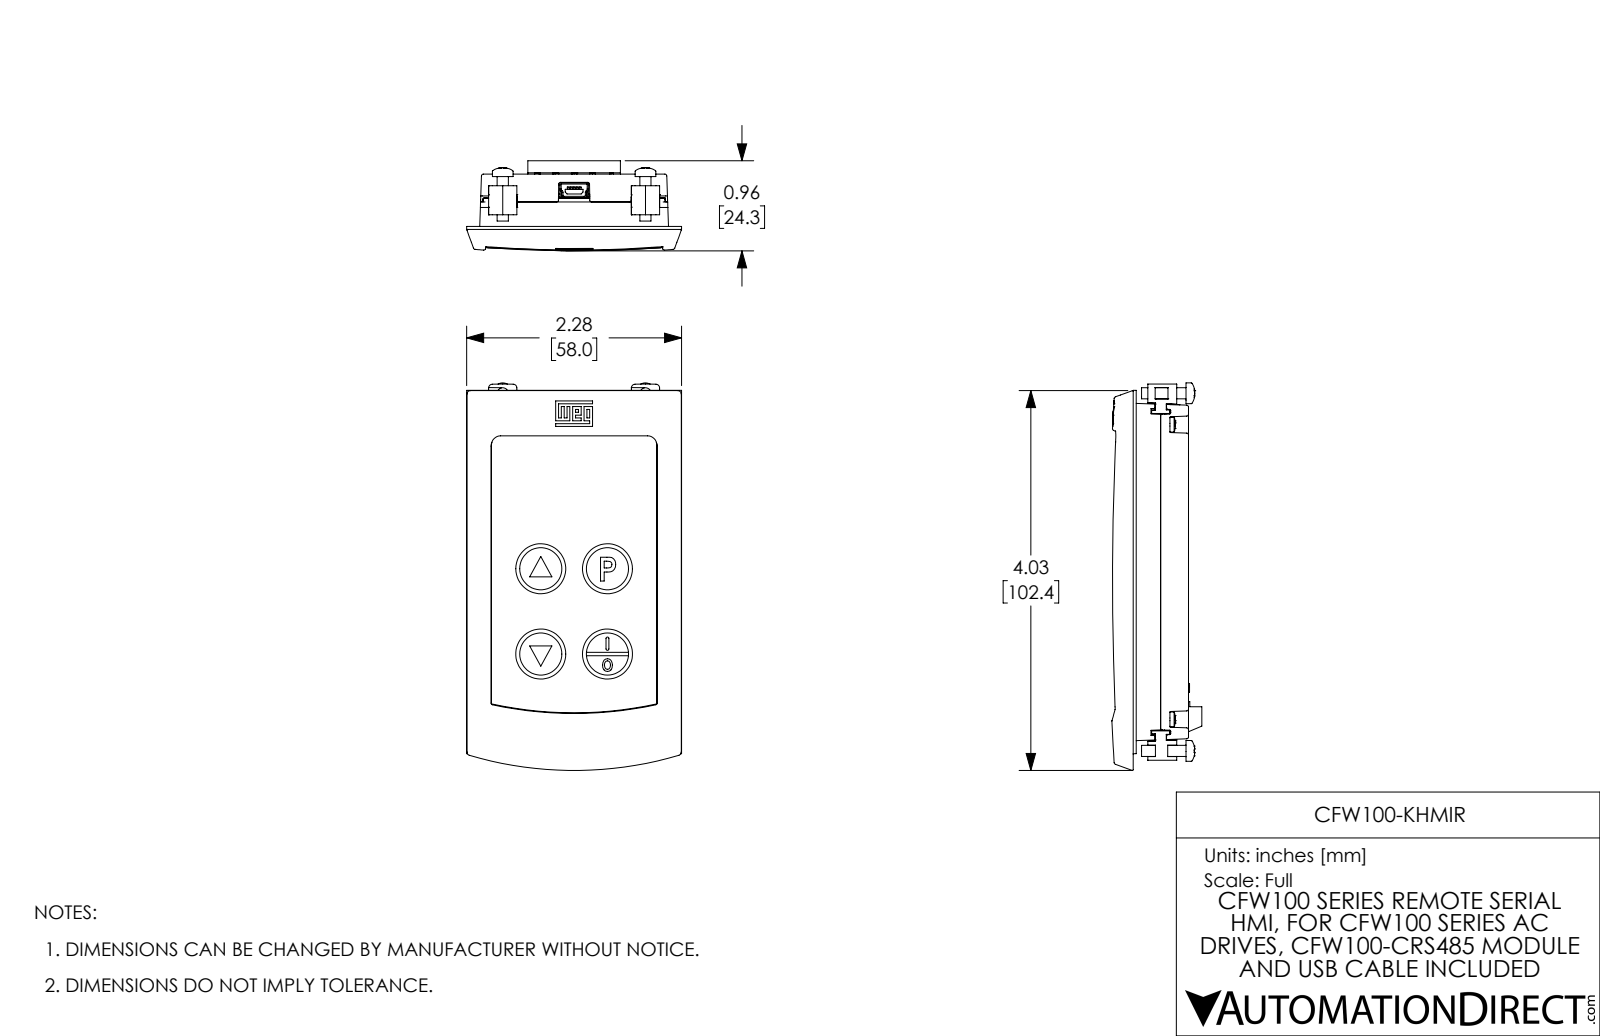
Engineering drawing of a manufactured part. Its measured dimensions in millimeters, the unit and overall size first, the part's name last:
Units: millimetres
Overall size (bounding box): 104.5 × 58 × 24.3
Round holes (diameter × count): ⌀4.5 ×6, ⌀2.5 ×5, ⌀3.8 ×5, ⌀0.9 ×4, ⌀3.8 ×2
Round bosses / shafts (diameter × count): ⌀5.6 ×4, ⌀4 ×4, ⌀3 ×4, ⌀1.4 ×4, ⌀0.8 ×2
Partial cylindrical surfaces — rounded edges, fillets, slot ends (radius × count): R0.3 ×322, R0.5 ×140, R0.2 ×43, R0.1 ×34, R0.3 ×33, R0.7 ×20, R1 ×13, R0.3 ×12
Main face-to-face distances: 8, 6.4, 1.6, 6.3, 4.7, 6.1, 14.1, 7.7, 1.7, 9.2
Hole centre spacings: 5, 5, 9.9, 4.4, 9.6, 10, 10, 10
Volume: 41 150 mm³ · Surface area: 53 030 mm²
Bodies: 6 solids, 4180 faces (1422 planar, 1094 cylindrical, 1664 other)
Part name (STEP PRODUCT): CFW100-KHMIR b1 cr1
STEP written by: SolidWorks 2017 (AUTOMOTIVE_DESIGN)
